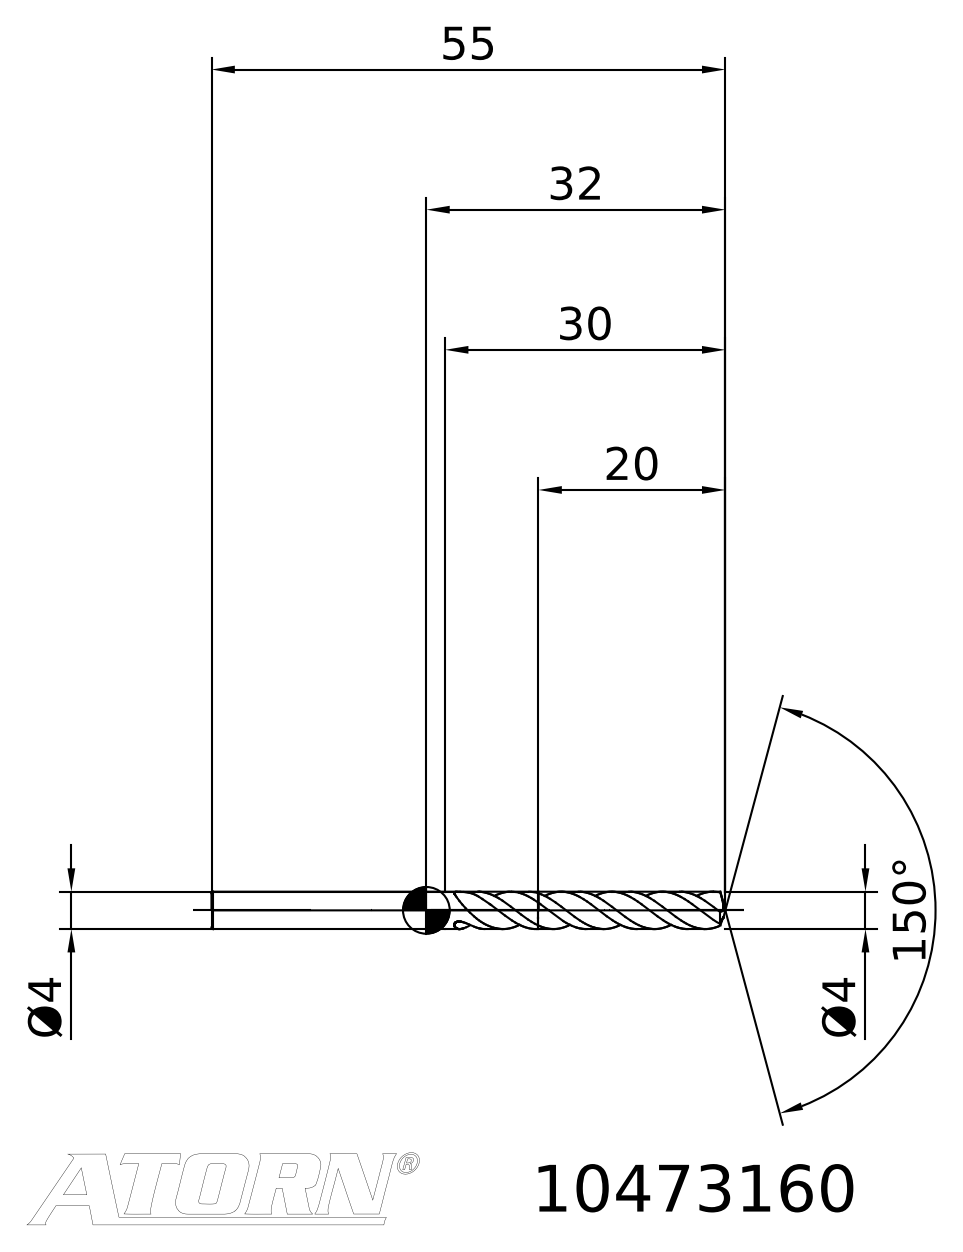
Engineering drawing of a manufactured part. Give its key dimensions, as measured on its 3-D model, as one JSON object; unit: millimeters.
{"step_written_by": "TDM (AUTOMOTIVE_DESIGN)", "units": "millimeters", "bodies": {"solids": 2, "faces": 36, "planar": 3, "cylindrical": 0, "other": 33}, "overall_size": [55, 5.68, 4.64], "volume_mm3": 508, "surface_area_mm2": 777, "face_to_face_distances": [35]}
